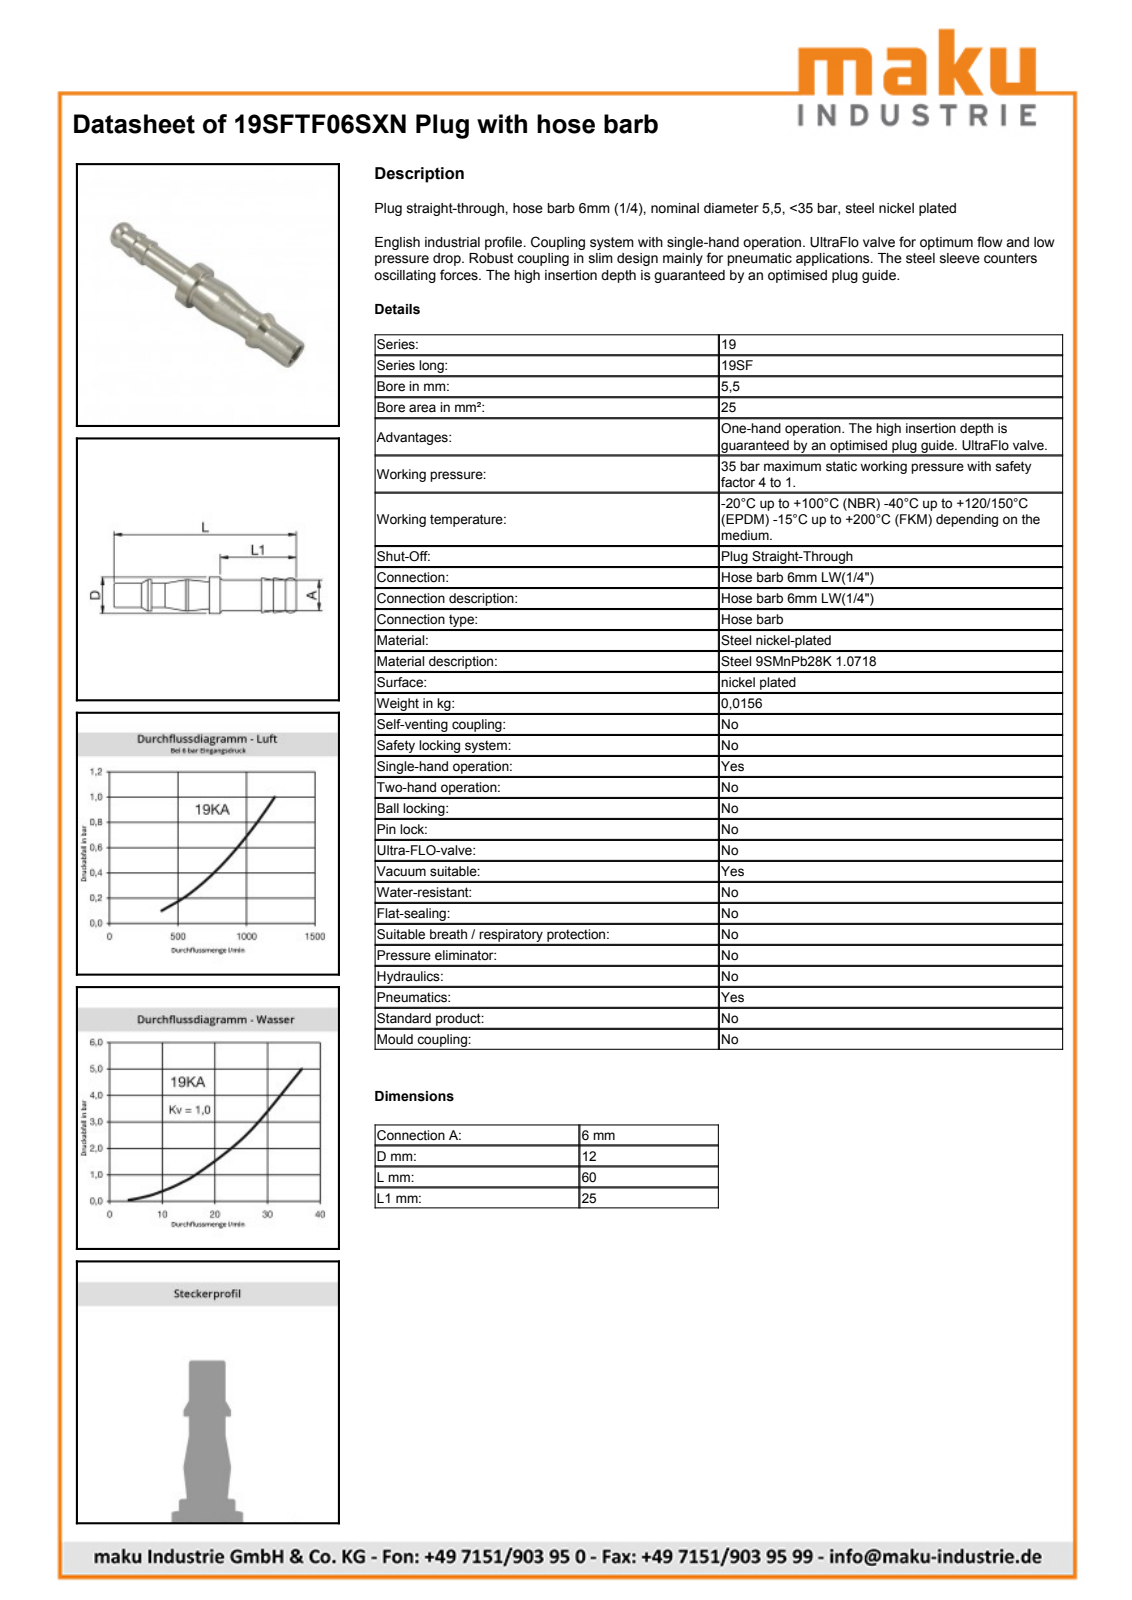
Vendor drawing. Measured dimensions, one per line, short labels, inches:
name: D112923
written by: Autodesk Inventor 2013 (AUTOMOTIVE_DESIGN)
unit: in
bodies: 1 solid, 29 faces (6 planar, 7 cylindrical, 16 other)
size: 2.362 × 0.472 × 0.472
volume: 0.123 in³; area: 4.109 in²
holes: 1× ⌀0.161, 1× ⌀0.217
bosses: 1× ⌀0.472, 1× ⌀0.407, 1× ⌀0.311, 1× ⌀0.24
face distances: 0.892, 0.144, 0.748, 1.378, 1.234, 0.486, 0.984, 1.128, 1.876, 2.362
